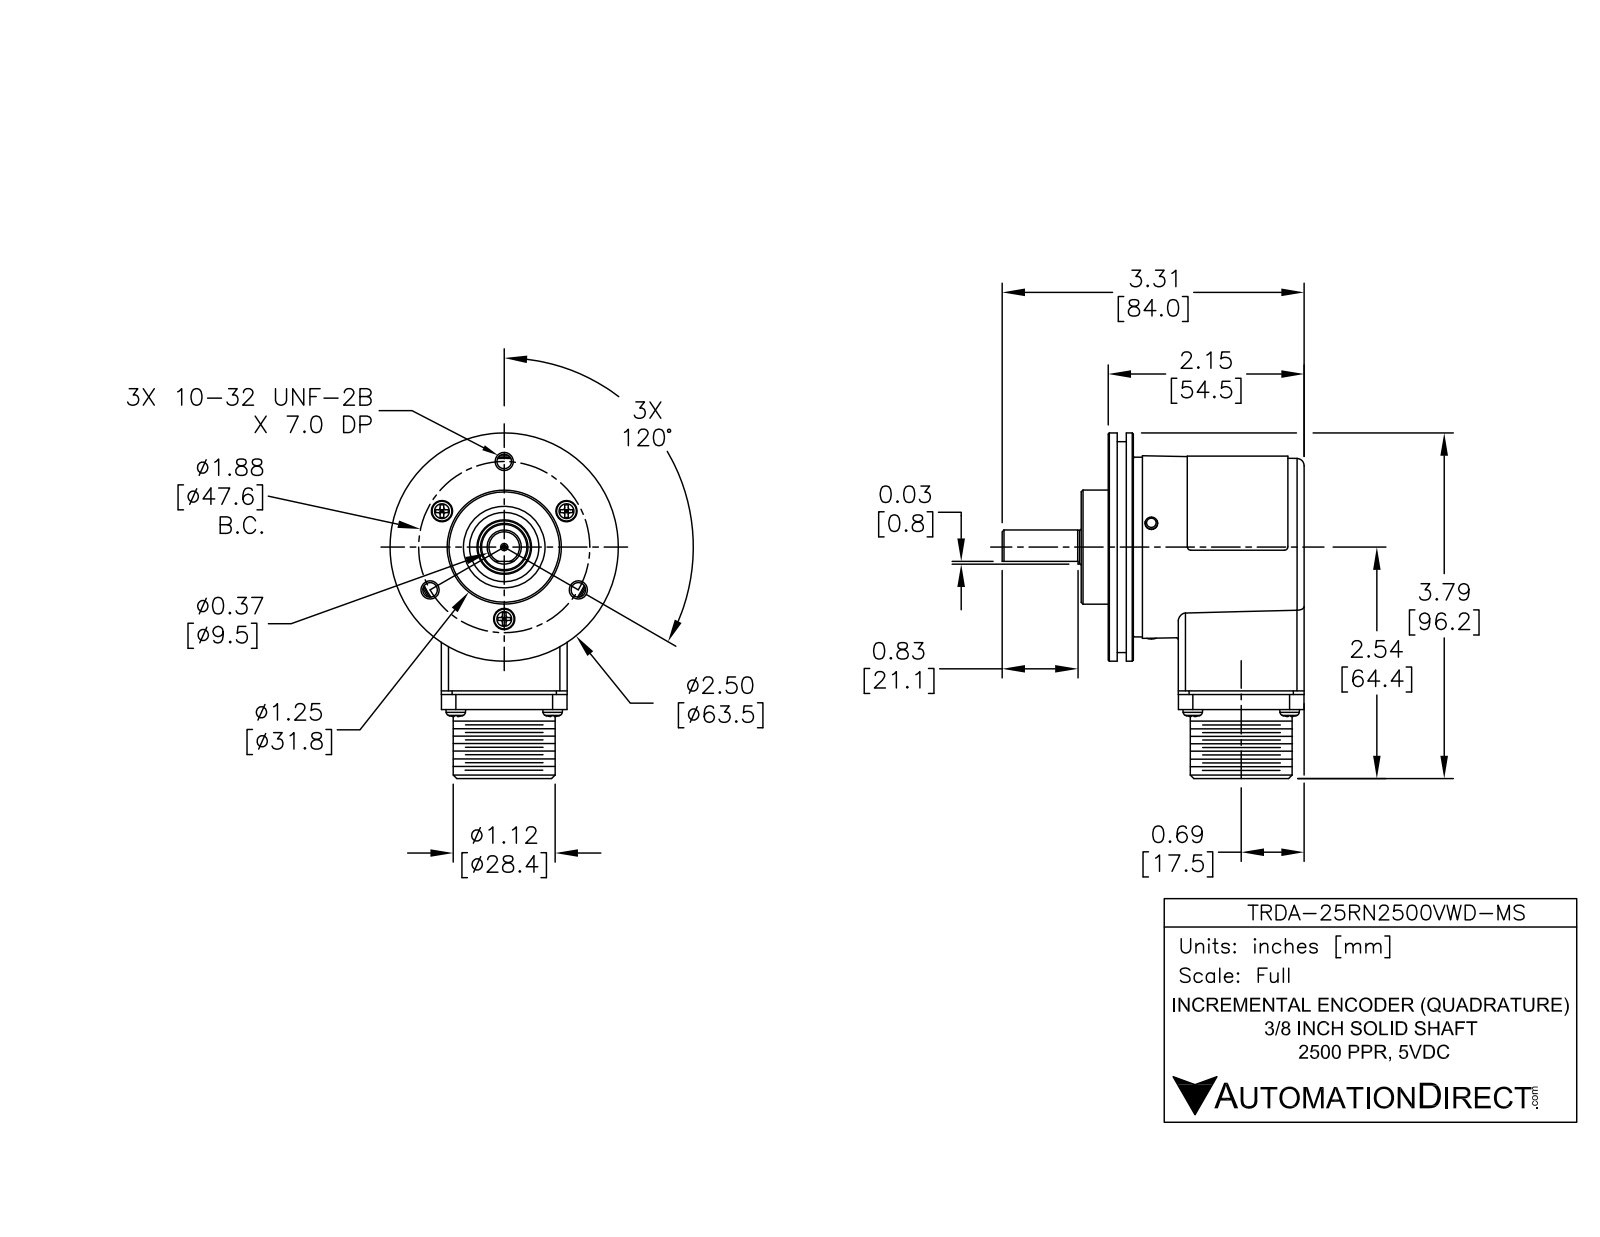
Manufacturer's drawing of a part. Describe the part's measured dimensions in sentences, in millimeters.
The part is named "TRDA-25RN-_WD-MS; MANIFOLD_SOLID_BREP_18486; ASSY_TRDA-25RN-VW-MS_SW0001_1_ASM". Its 3-D file was written by "SolidWorks 2016 (AUTOMOTIVE_DESIGN)". It is 1 solid with 450 faces: 211 planar, 117 cylindrical and 122 other. Overall it measures 96.15 by 84 by 63.5 millimeters. Its volume is 151 854 cubic millimeters and its surface area 27 000 square millimeters. Round holes: 3 of diameter 2.2, 3 of diameter 4.04, 3 of diameter 5.5, 1 of diameter 1.2, 1 of diameter 20.3, 1 of diameter 22.15, 1 of diameter 23.8, 1 of diameter 32. Round bosses or shafts: 10 of diameter 1.6, 3 of diameter 2, 1 of diameter 63.5, 1 of diameter 58.67, 1 of diameter 50, 1 of diameter 31.75, 1 of diameter 28.35, 1 of diameter 13. Partial cylindrical surfaces (rounded edges, fillets, slot ends): 31 of radius 0.5, 4 of radius 2, 4 of radius 3, 4 of radius 4, 1 of radius 24.39. The main face-to-face distances are 54.5, 7, 47.5, 35, 17, 2.5, 12.5, 19.5, 12.54, 14.5. The hole center spacings are 22.16, 20, 34.64, 22.15, 23.81, 41.25, 43.81, 23.82.
